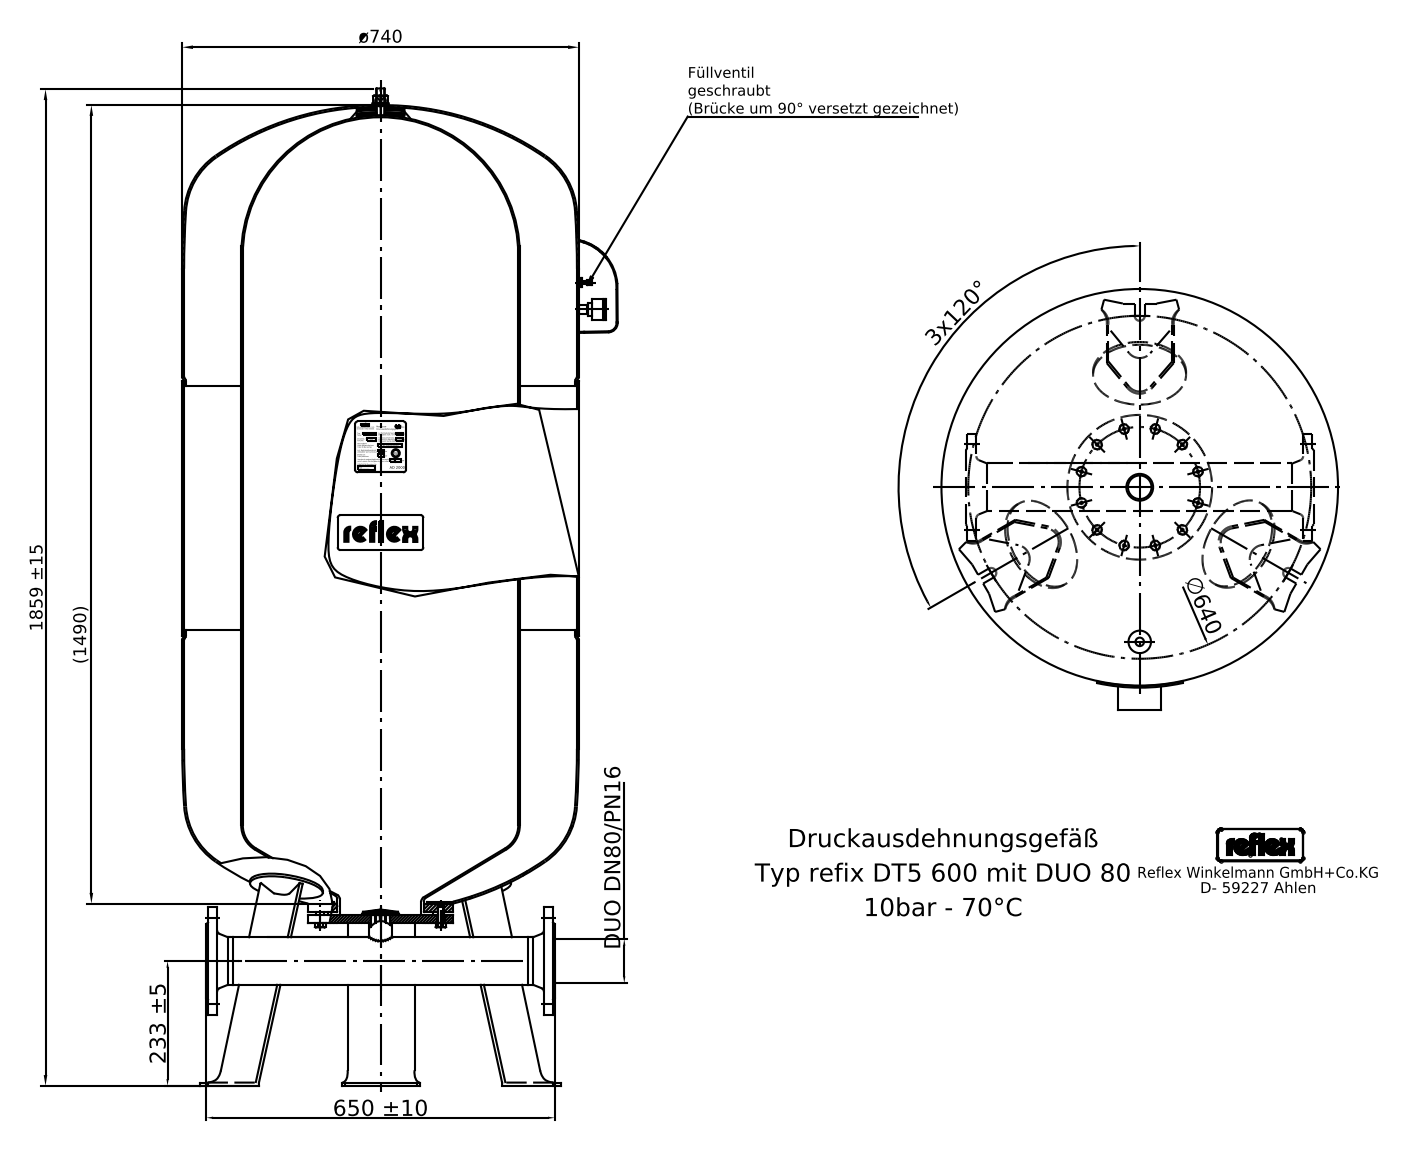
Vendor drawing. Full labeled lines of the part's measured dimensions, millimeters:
STEP written by: Mechanical Desktop 2008 (CONFIG_CONTROL_DESIGN)
Units: millimetres
Bodies: 26 solids, 538 faces (233 planar, 163 cylindrical, 142 other)
Overall size (bounding box): 1859 × 810.1 × 740
Volume: 599 100 000 mm³ · Surface area: 6 832 000 mm²
Round holes (diameter × count): ⌀19 ×8, ⌀2.48 ×1, ⌀3.8 ×1, ⌀4.3 ×1, ⌀4.4 ×1, ⌀5.45 ×1, ⌀7 ×1, ⌀8 ×1, ⌀11.4 ×1, ⌀88.9 ×1, ⌀157 ×1, ⌀250 ×1
Round bosses / shafts (diameter × count): ⌀10 ×9, ⌀740 ×1, ⌀260 ×1, ⌀230 ×1, ⌀200 ×1, ⌀62 ×1, ⌀42.4 ×1, ⌀34 ×1
Partial cylindrical surfaces — rounded edges, fillets, slot ends (radius × count): R25 ×18, R5.62 ×4, R2.25 ×3, R9 ×3, R3.84 ×2, R6.75 ×2, R8 ×2, R9.27 ×2
Main face-to-face distances: 1127, 6, 195, 1322, 5.97, 5.89, 201, 1328, 313, 5
Hole centre spacings: 80, 113.13, 61.22, 61.24, 147.81, 147.82, 160, 50
